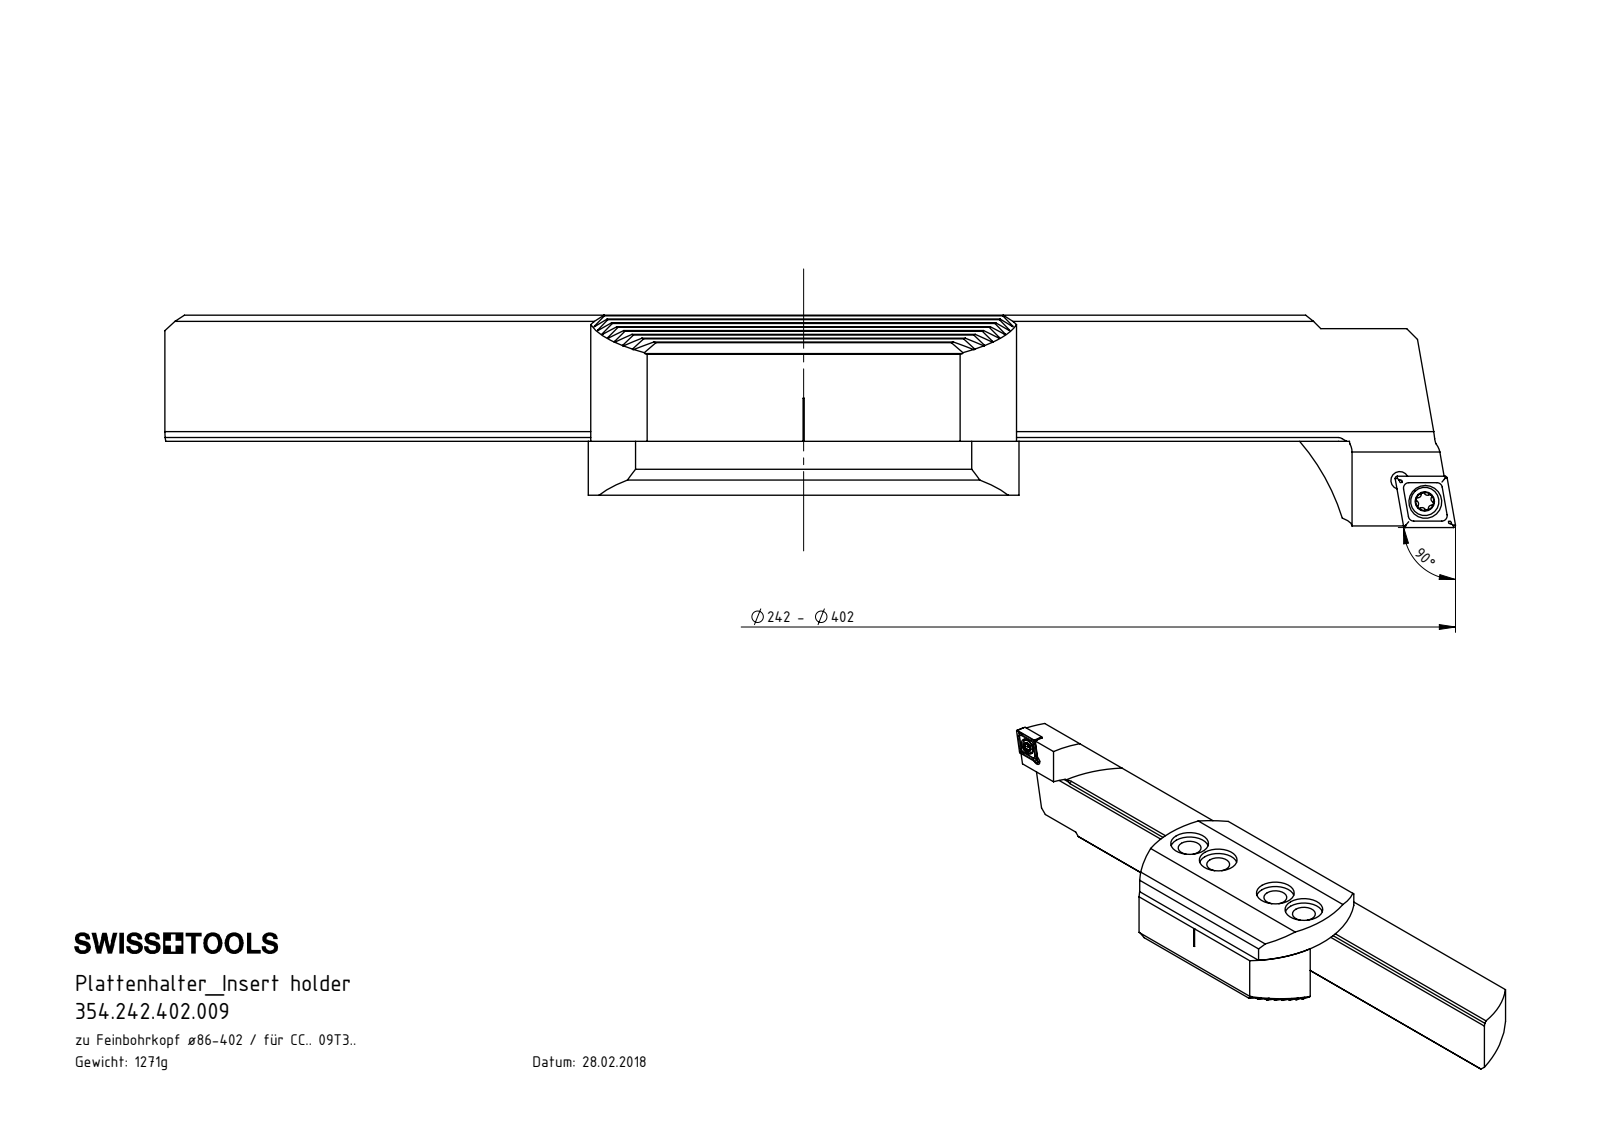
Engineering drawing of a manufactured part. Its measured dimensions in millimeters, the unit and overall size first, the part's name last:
Units: millimetres
Overall size (bounding box): 239.57 × 55 × 39.4
Round holes (diameter × count): ⌀8.5 ×4, ⌀14 ×4, ⌀3.3 ×2, ⌀4.4 ×1, ⌀6.1 ×1
Round bosses / shafts (diameter × count): ⌀5.25 ×1, ⌀4 ×1
Partial cylindrical surfaces — rounded edges, fillets, slot ends (radius × count): R0.2 ×16, R0.34 ×6, R0.59 ×6, R40 ×6, R0.8 ×1
Main face-to-face distances: 2.38, 4.76, 21.3, 7.14, 33.7, 9.52, 4.77, 7.15, 9.53, 11.91
Hole centre spacings: 15, 45, 6.06, 6.19, 30, 60
Volume: 161 949 mm³ · Surface area: 41 929 mm²
Bodies: 5 solids, 992 faces (604 planar, 67 cylindrical, 321 other)
Part name (STEP PRODUCT): F00-WCB.136.002_A; F00-WCB.136.003_A; WCB-ER2.001.009_A; F00-WCB.242.001 (+3 more)
STEP written by: SolidWorks 2017 (CONFIG_CONTROL_DESIGN)
